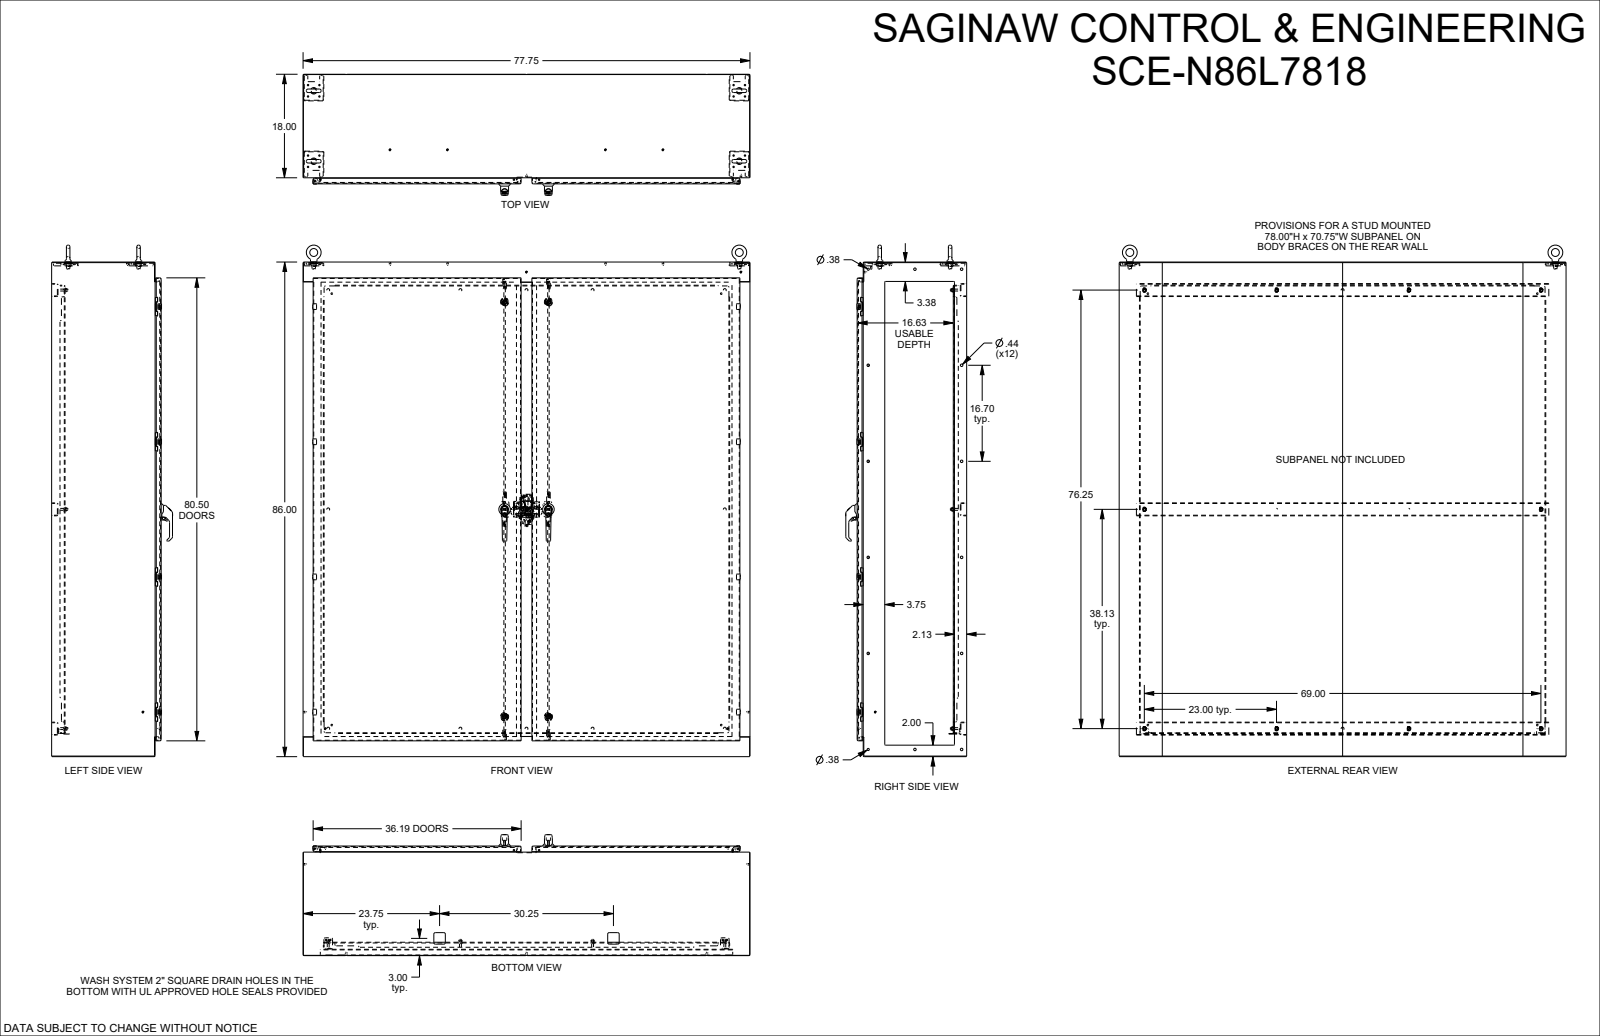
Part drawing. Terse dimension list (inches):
name: SCE-N86L7818
written by: SolidWorks 2023 (AUTOMOTIVE_DESIGN)
unit: in
bodies: 48 solids, 7310 faces (3016 planar, 2462 cylindrical, 1832 other)
size: 88.945 × 77.75 × 21.046
volume: 2 233 in³; area: 42 429 in²
holes: 20× ⌀0.25, 18× ⌀0.375, 16× ⌀0.205, 16× ⌀0.244, 12× ⌀0.437, 8× ⌀0.04, 8× ⌀0.17, 8× ⌀0.218, 4× ⌀0.256, 4× ⌀0.343, 4× ⌀0.344, 4× ⌀0.36
bosses: 24× ⌀0.17, 20× ⌀0.25, 16× ⌀0.24, 10× ⌀0.196, 4× ⌀1.4, 4× ⌀1.173, 4× ⌀0.6, 4× ⌀0.341
rounds: 196× R0.03, 166× R0.015, 100× R0.125, 72× R0.02, 48× R0.02, 44× R0.25, 42× R0.039, 40× R0.04
face distances: 0.104, 18.954, 19.058, 18.85, 17.896, 1.058, 85.896, 17.792, 1.162, 86
hole spacings: 1.979, 23.5, 1.4, 16.7, 23.302, 47, 33.4, 37.143
